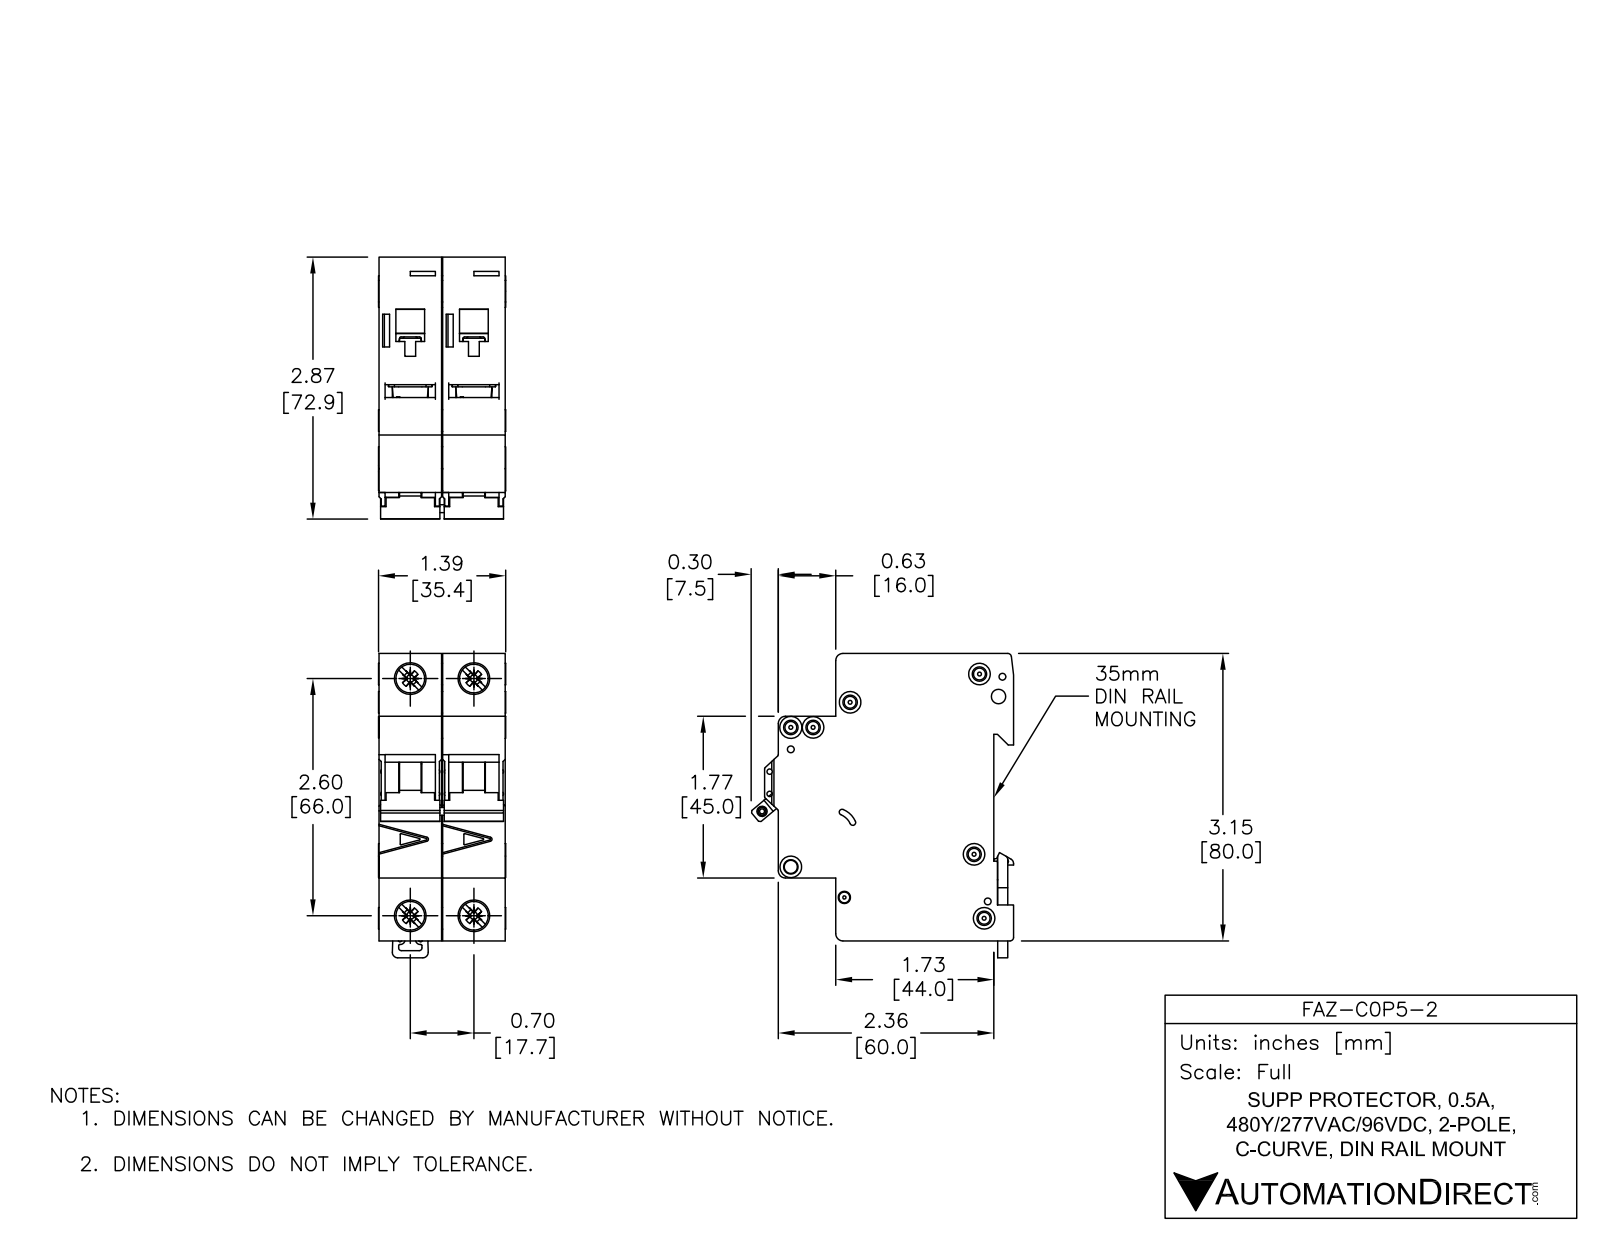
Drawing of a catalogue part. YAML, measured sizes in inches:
part_name: "FAZ-C0P5-2"
step_written_by: "SolidWorks 2014 (AUTOMOTIVE_DESIGN)"
units: inches
bodies: {solids: 8, faces: 1104, planar: 466, cylindrical: 396, other: 242}
overall_size: [3.338, 2.876, 1.394]
volume: 9.142
surface_area: 60.14
round_holes:
  - {diameter: 0.142, count: 6}
  - {diameter: 0.075, count: 3}
  - {diameter: 0.043, count: 2}
  - {diameter: 0.059, count: 2}
  - {diameter: 0.157, count: 2}
  - {diameter: 0.281, count: 2}
  - {diameter: 0.323, count: 2}
  - {diameter: 0.085, count: 1}
  - {diameter: 0.087, count: 1}
  - {diameter: 0.1, count: 1}
  - {diameter: 0.13, count: 1}
  - {diameter: 0.134, count: 1}
round_bosses_or_shafts:
  - {diameter: 0.236, count: 4}
  - {diameter: 0.323, count: 2}
  - {diameter: 0.098, count: 2}
partial_cylinders:
  - {radius: 0.01, count: 49}
  - {radius: 0.02, count: 19}
  - {radius: 0.079, count: 10}
  - {radius: 0.008, count: 8}
  - {radius: 0.039, count: 8}
  - {radius: 0.031, count: 2}
  - {radius: 0.071, count: 2}
  - {radius: 0.118, count: 2}
face_to_face_distances: [0.697, 0.689, 1.386, 3.129, 0.217, 1.949, 1.732, 2.579, 2.362, 0.63]
hole_center_spacings: [0.244, 0.537, 0.697, 2.598, 2.69, 0.189, 0.204, 0.221]
